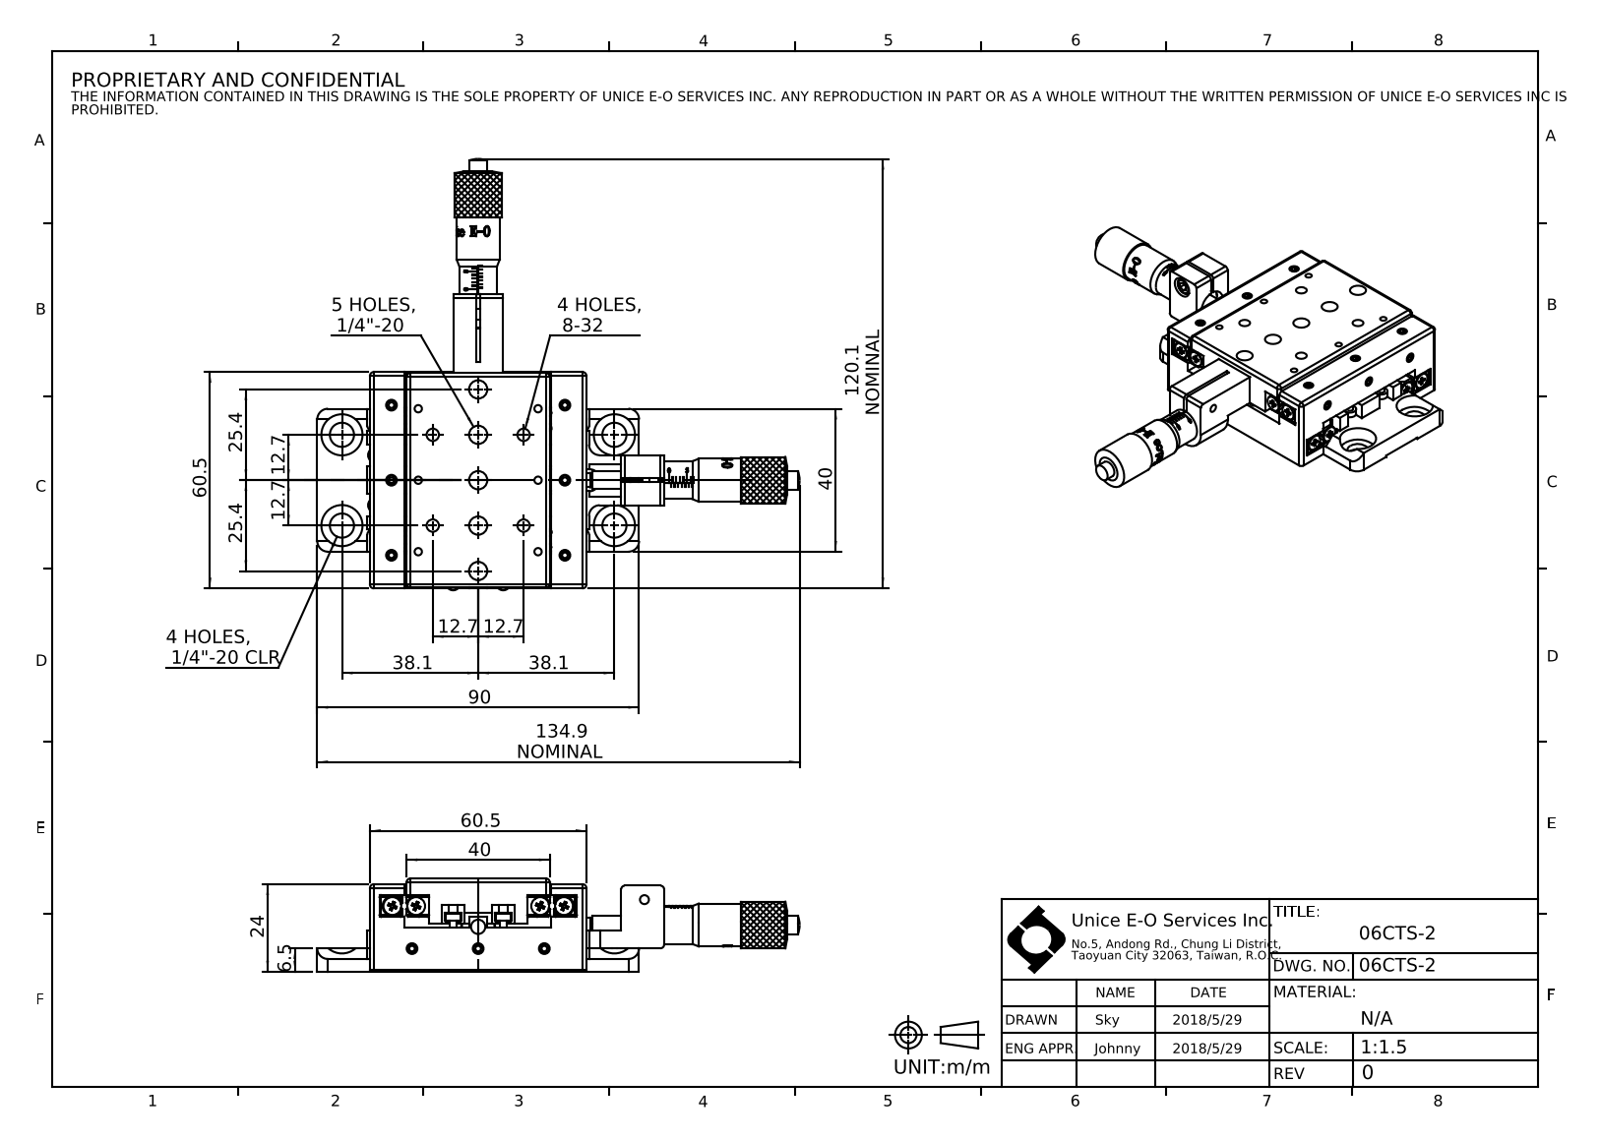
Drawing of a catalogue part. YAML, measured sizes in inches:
part_name: "06CTS-2"
step_written_by: "SolidWorks 2016 (AUTOMOTIVE_DESIGN)"
units: inches
bodies: {solids: 0, faces: 1059, planar: 650, cylindrical: 233, other: 176}
overall_size: [5.311, 4.752, 1.024]
round_holes:
  - {diameter: 0.081, count: 12}
  - {diameter: 0.098, count: 8}
  - {diameter: 0.201, count: 5}
  - {diameter: 0.136, count: 4}
  - {diameter: 0.266, count: 4}
  - {diameter: 0.453, count: 4}
  - {diameter: 0.063, count: 2}
  - {diameter: 0.256, count: 2}
  - {diameter: 0.374, count: 2}
  - {diameter: 0.417, count: 2}
  - {diameter: 0.157, count: 1}
  - {diameter: 0.315, count: 1}
round_bosses_or_shafts:
  - {diameter: 0.197, count: 10}
  - {diameter: 0.157, count: 5}
  - {diameter: 0.079, count: 4}
  - {diameter: 0.512, count: 2}
  - {diameter: 0.472, count: 2}
  - {diameter: 0.413, count: 2}
  - {diameter: 0.362, count: 2}
  - {diameter: 0.205, count: 2}
partial_cylinders:
  - {radius: 0.039, count: 20}
  - {radius: 0.118, count: 6}
  - {radius: 0.059, count: 4}
  - {radius: 0.235, count: 2}
  - {radius: 0.276, count: 1}
face_to_face_distances: [0.118, 0.236, 0.65, 0.122, 0.465, 0.354, 0.374, 0.346, 0.197, 0.266]
hole_center_spacings: [1, 1.581, 0.329, 0.5, 0.525, 0.672, 0.707, 0.787]
